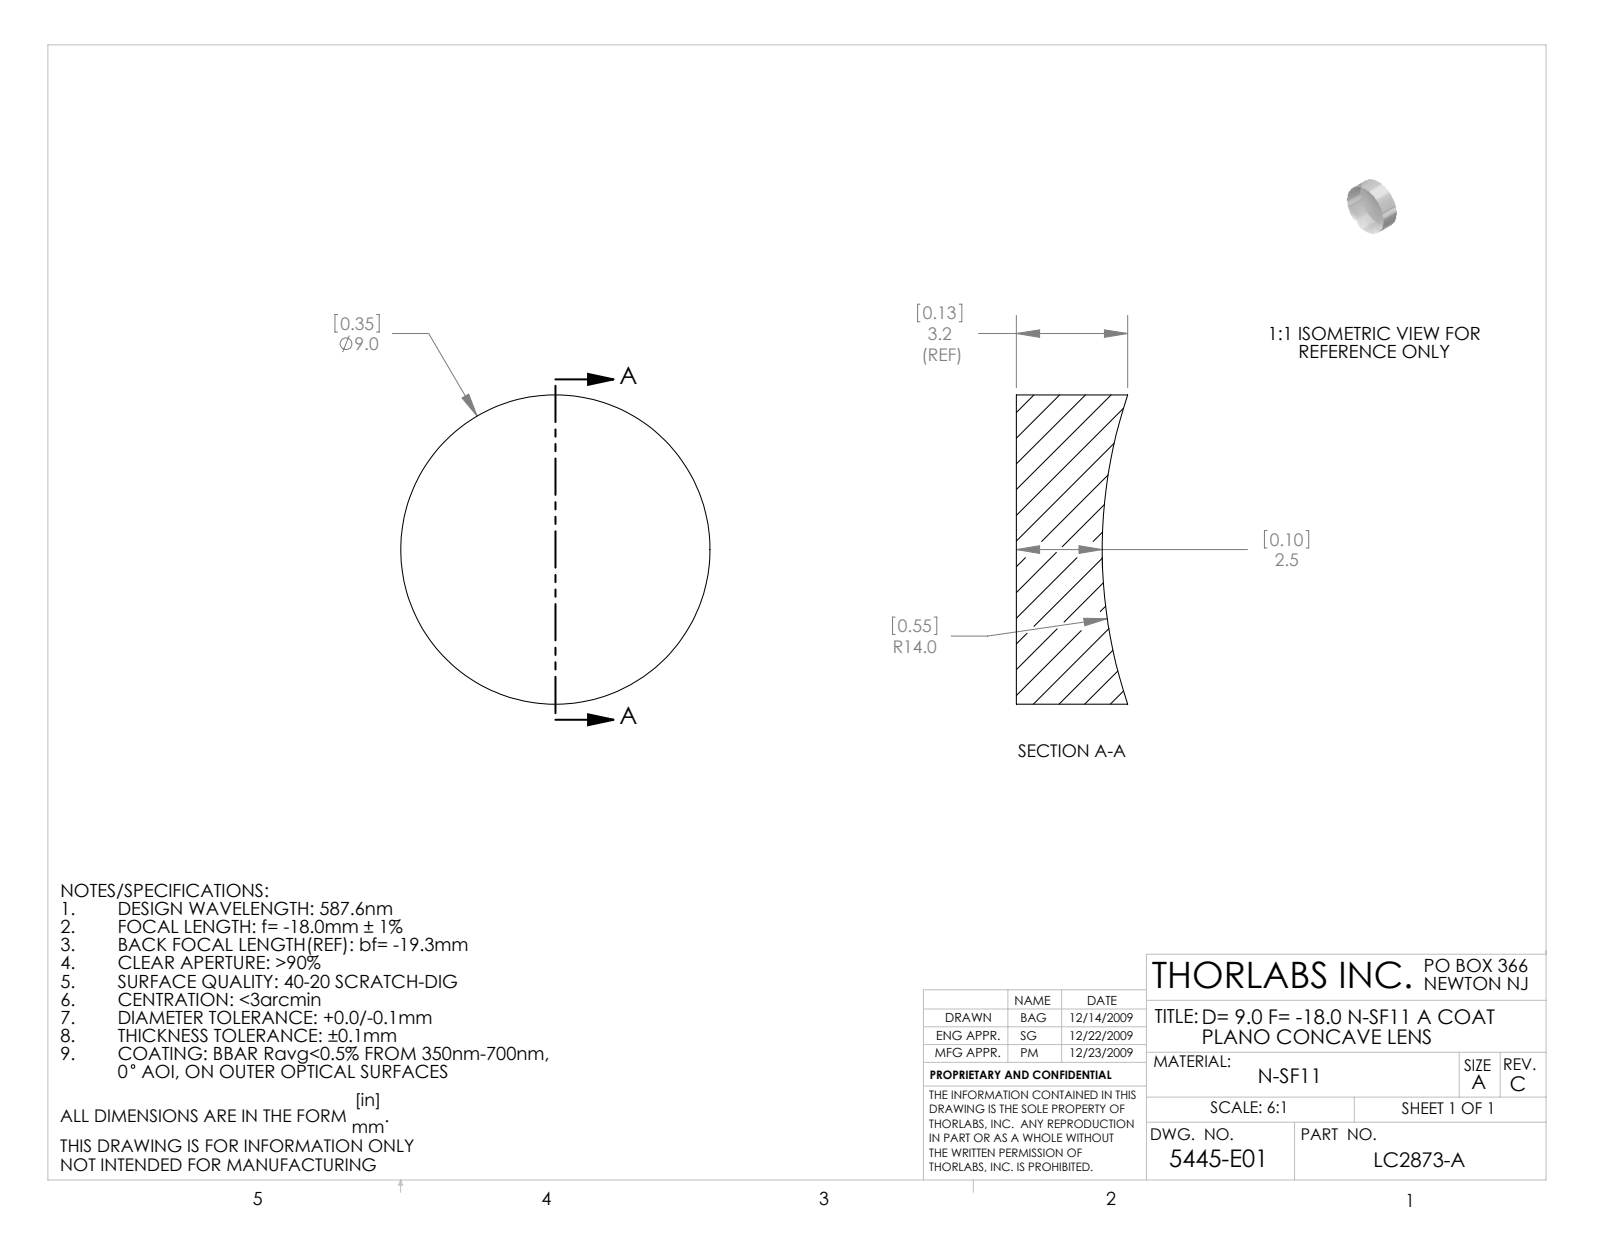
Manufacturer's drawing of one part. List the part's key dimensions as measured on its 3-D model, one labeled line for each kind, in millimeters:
Part name (STEP PRODUCT): 5445-E0W
STEP written by: SolidWorks 2009 (AUTOMOTIVE_DESIGN)
Units: millimetres
Bodies: 1 solid, 5 faces (1 planar, 2 cylindrical, 2 other)
Overall size (bounding box): 9 × 9 × 3.3
Volume: 180 mm³ · Surface area: 221 mm²
Round bosses / shafts (diameter × count): ⌀9 ×1
